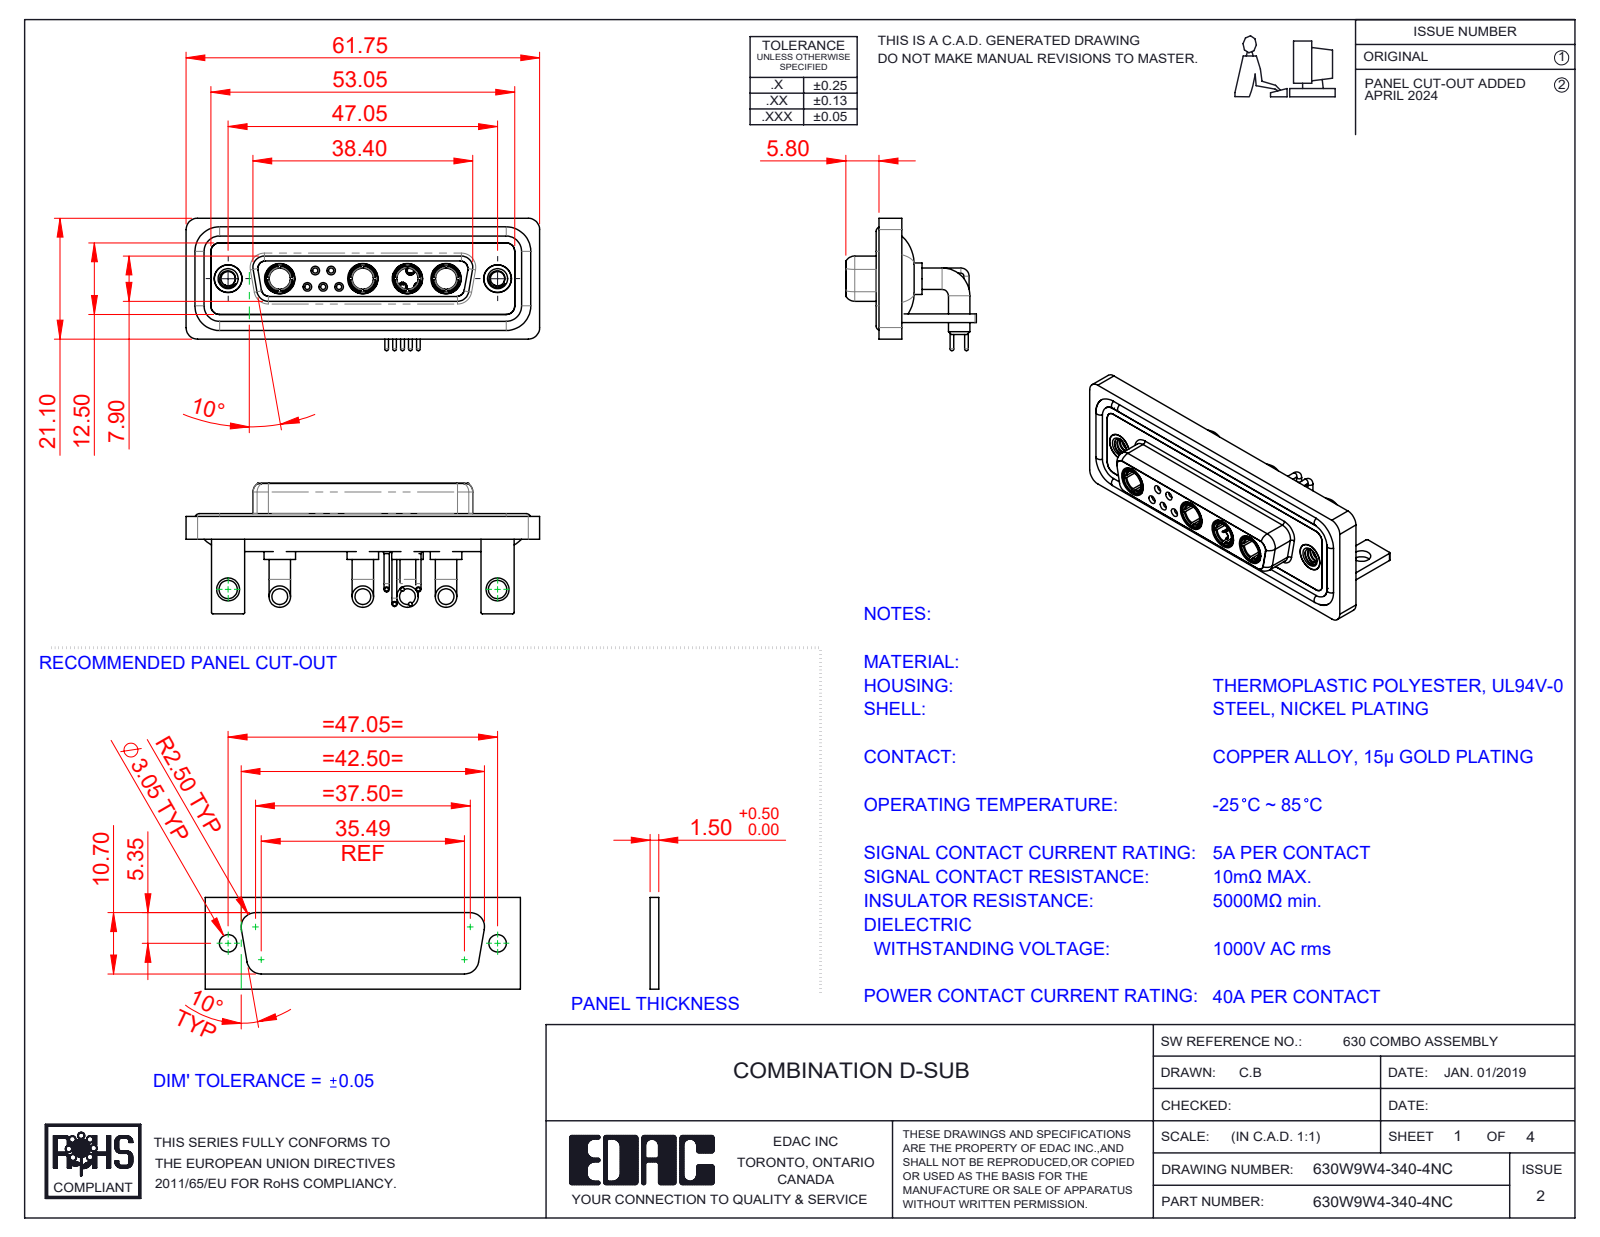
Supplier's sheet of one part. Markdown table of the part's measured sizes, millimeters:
| quantity | value |
| --- | --- |
| part name | 630Combo Threaded Rivet_A; 630Combo Contact Row 2_50 Contacts; 630Combo Contact Row 1_50 Contacts; 630Combo Stabilizer Bracket_50 Contacts (+6 more) |
| STEP written by | SolidWorks 2023 (CONFIG_CONTROL_DESIGN) |
| units | millimeters |
| bodies | 22 solids, 1005 faces (316 planar, 425 cylindrical, 264 other) |
| overall size | 61.75 × 23.12 × 22.8 |
| volume | 9 102 mm³ |
| surface area | 14 961 mm² |
| round holes (diameter × count) | 4.85 × 6, 0.9 × 5, 1.1 × 5, 1.5 × 5, 2 × 5, 3.7 × 4, 5.3 × 4, 1.6 × 3, 1.7 × 2, 2.5 × 2, 3.2 × 2, 4 × 2 |
| round bosses / shafts (diameter × count) | 0.9 × 10, 1.6 × 9, 3.75 × 8, 2 × 5, 1.5 × 5, 0.65 × 5, 5.5 × 4, 5.2 × 4 |
| partial cylindrical surfaces (radius × count) | 2 × 19, 1.5 × 18, 0.25 × 16, 1.35 × 8, 1.6 × 8, 0.5 × 5, 0.6 × 4, 0.65 × 4 |
| main face-to-face distances | 0.4, 1.8, 2.9, 3.7, 1.5, 4.1, 1.1, 1.4, 1.6, 2.5 |
| hole center spacings | 3.16, 2.77, 5.04, 13.85, 11.08, 12.79, 15.5, 5.54 |
